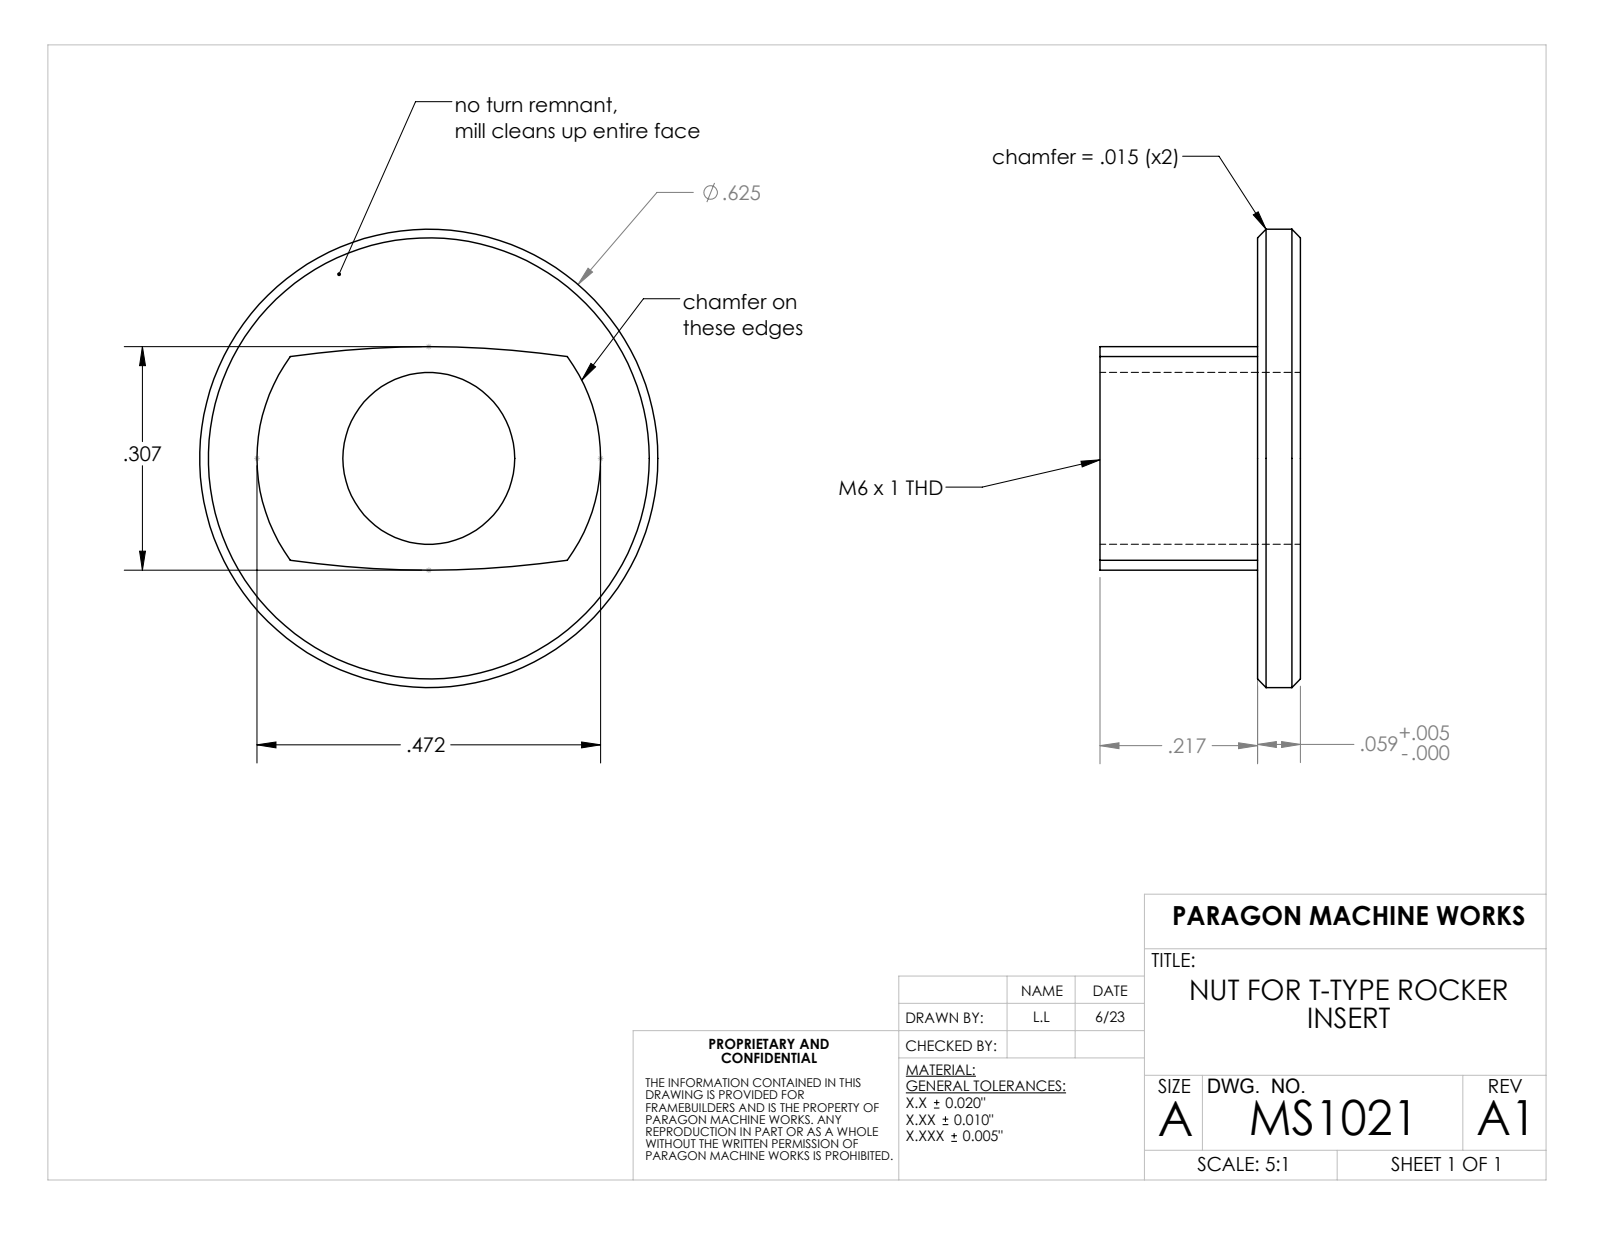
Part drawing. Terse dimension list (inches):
name: MS1021
written by: SolidWorks 2022 (AUTOMOTIVE_DESIGN)
unit: in
bodies: 1 solid, 12 faces (3 planar, 9 cylindrical, 0 other)
size: 0.63 × 0.63 × 0.276
volume: 0.035 in³; area: 1.15 in²
holes: 1× ⌀0.236
bosses: 1× ⌀0.63
rounds: 2× R1.339, 1× R0.236
face distances: 0.059, 0.276, 0.217
